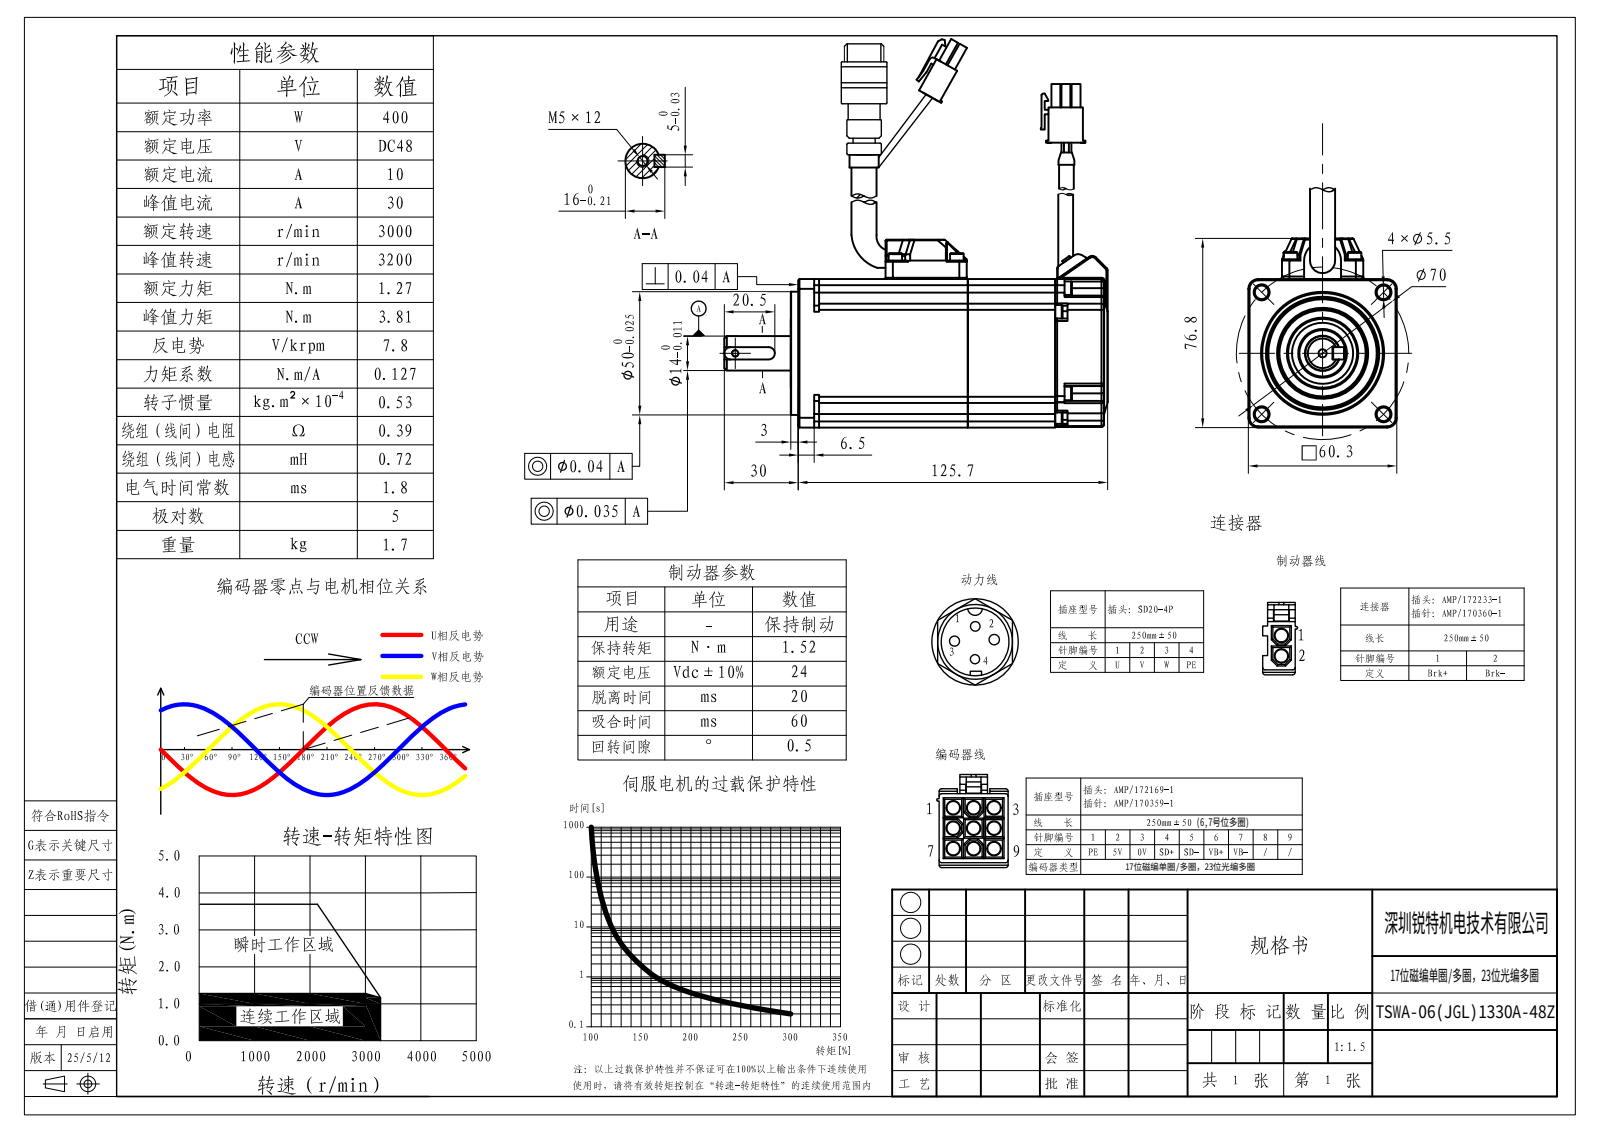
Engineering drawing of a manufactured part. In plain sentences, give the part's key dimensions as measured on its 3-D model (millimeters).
The part is named "LMZ-04B06030D12-A". Its 3-D file was written by "SolidWorks 2018 (CONFIG_CONTROL_DESIGN)". It is 22 solids with 1099 faces: 443 planar, 435 cylindrical and 221 other. Overall it measures 155.7 by 72.8 by 60.3 millimeters. Its volume is 174 052 cubic millimeters and its surface area 97 781 square millimeters. Round holes: 22 of diameter 2, 9 of diameter 2.5, 8 of diameter 3.5, 4 of diameter 5.5, 2 of diameter 2.8, 2 of diameter 3.3, 1 of diameter 2.05, 1 of diameter 4.2, 1 of diameter 6, 1 of diameter 6.3, 1 of diameter 7.6, 1 of diameter 9. Round bosses or shafts: 10 of diameter 5.5, 10 of diameter 3, 2 of diameter 4, 2 of diameter 2.2, 2 of diameter 2, 1 of diameter 58.5, 1 of diameter 54, 1 of diameter 50. Partial cylindrical surfaces (rounded edges, fillets, slot ends): 36 of radius 1, 26 of radius 2.5, 25 of radius 2, 24 of radius 0.5, 12 of radius 3, 9 of radius 0.6, 8 of radius 4.5, 4 of radius 4. The main face-to-face distances are 60.3, 1.5, 18.3, 10, 3, 50.3, 21.3, 50.15, 125.7, 60.15. The hole center spacings are 8.29, 31.5, 41.49, 44.54, 52.09, 66.07, 0.49, 8.46.
